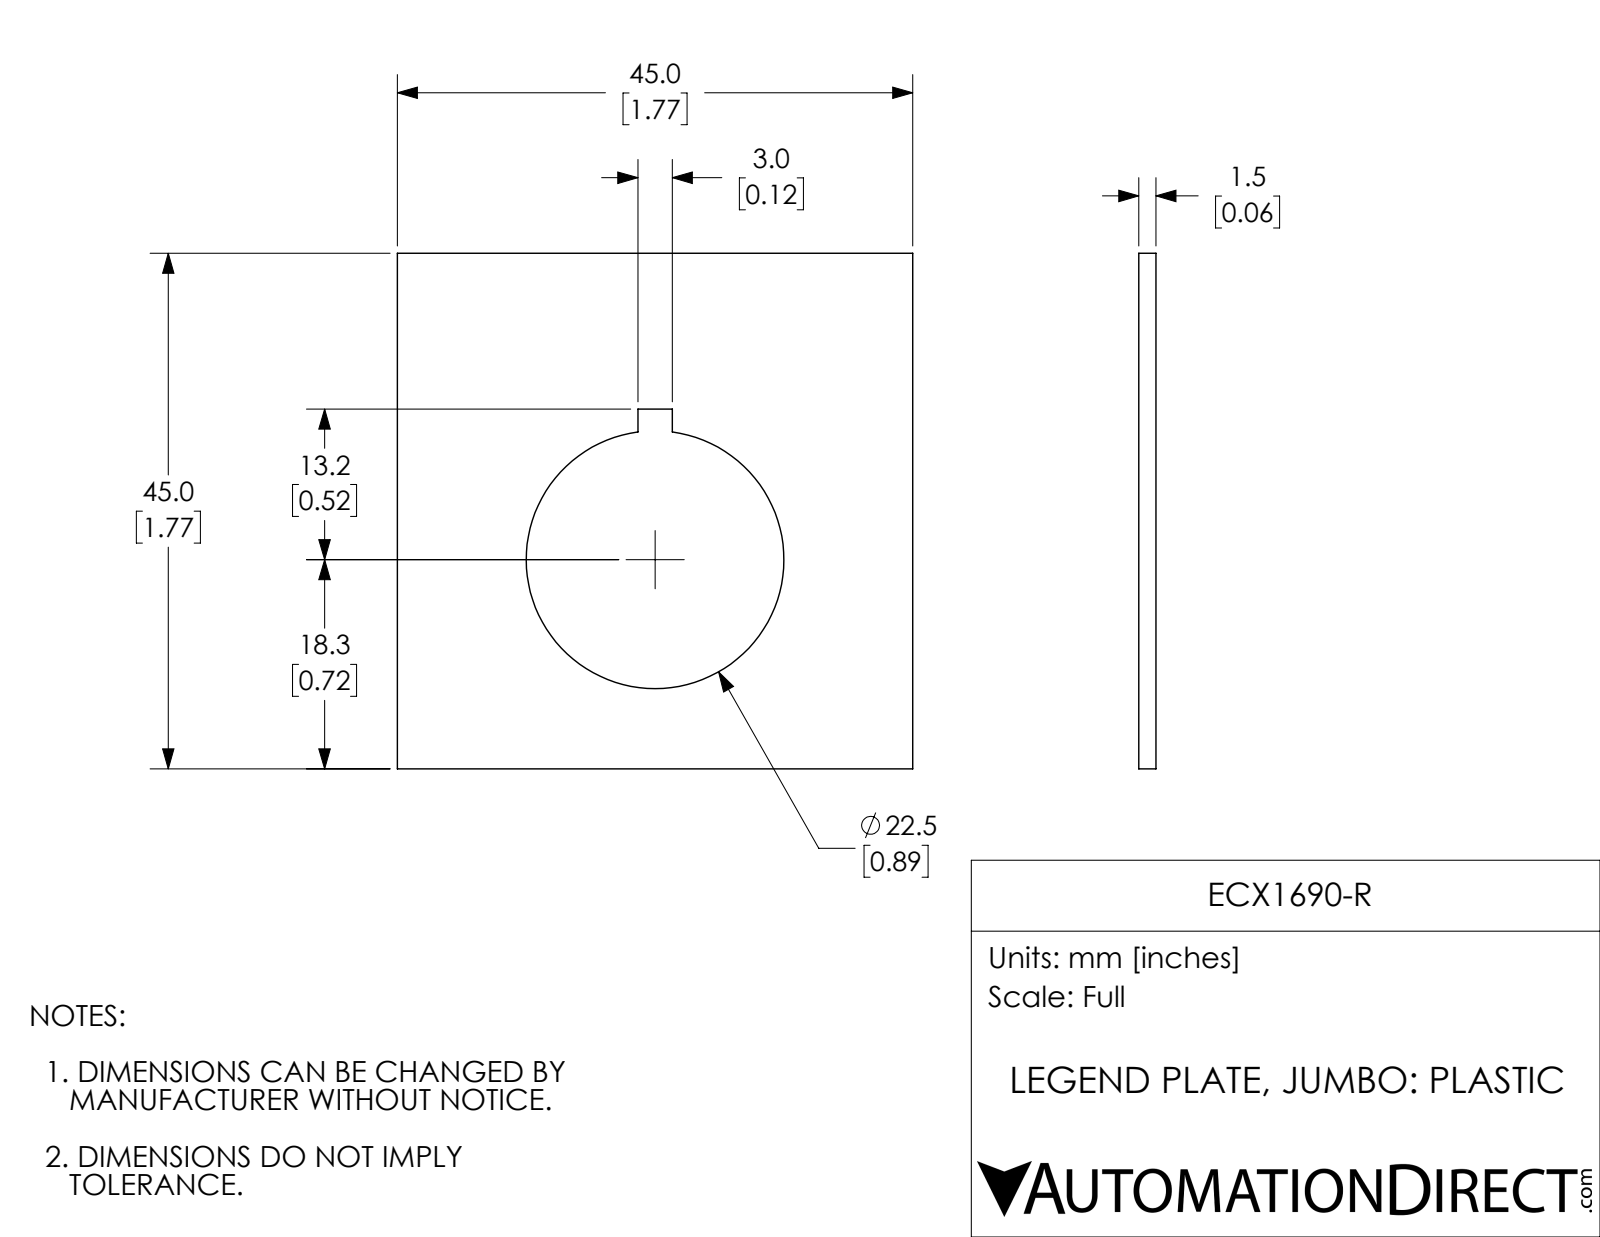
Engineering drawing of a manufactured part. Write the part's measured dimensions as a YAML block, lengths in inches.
part_name: "ECX1690-R"
step_written_by: "SolidWorks 2018 (AUTOMOTIVE_DESIGN)"
units: inches
bodies: {solids: 1, faces: 12, planar: 9, cylindrical: 3, other: 0}
overall_size: [1.772, 1.772, 0.059]
volume: 0.148
surface_area: 5.619
round_holes:
  - {diameter: 0.886, count: 1}
face_to_face_distances: [0.059, 1.772, 0.827, 0.945, 1.236, 0.535, 0.118]
